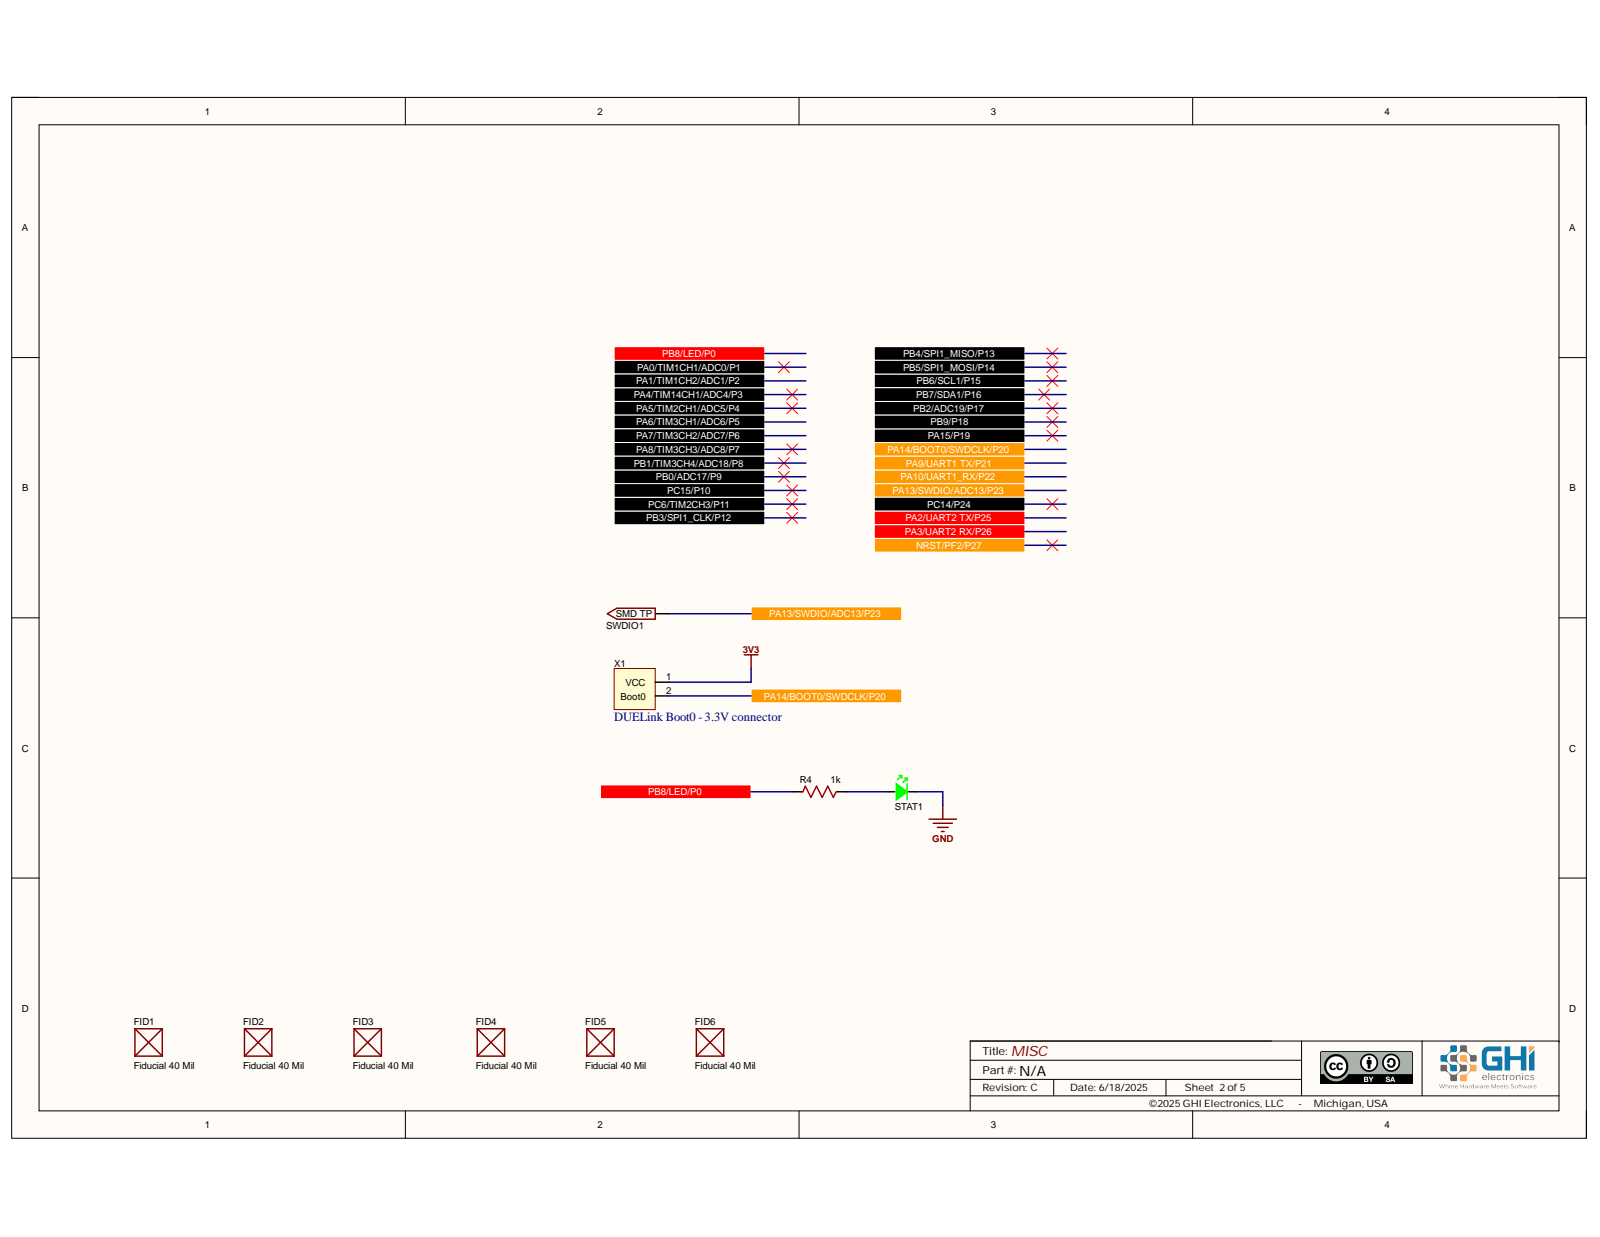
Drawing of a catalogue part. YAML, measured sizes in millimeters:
part_name: "PCB; Board; STAT1; 0603 LED Green (+4 more)"
step_written_by: "Open CASCADE 7.5 (AUTOMOTIVE_DESIGN)"
units: millimeters
bodies: {solids: 165, faces: 2469, planar: 1798, cylindrical: 417, other: 254}
overall_size: [27, 26.12, 22]
volume: 1612
surface_area: 4591
round_holes:
  - {diameter: 1, count: 9}
  - {diameter: 0.8, count: 7}
  - {diameter: 0.55, count: 4}
  - {diameter: 0.7, count: 4}
  - {diameter: 3, count: 4}
  - {diameter: 1.02, count: 2}
  - {diameter: 0.86, count: 1}
  - {diameter: 6, count: 1}
round_bosses_or_shafts:
  - {diameter: 1.1, count: 4}
  - {diameter: 11, count: 1}
  - {diameter: 9, count: 1}
  - {diameter: 0.95, count: 1}
partial_cylinders:
  - {radius: 0.12, count: 35}
  - {radius: 0.15, count: 26}
  - {radius: 0.2, count: 10}
  - {radius: 0.4, count: 9}
  - {radius: 0.9, count: 7}
  - {radius: 0.3, count: 6}
  - {radius: 0.38, count: 4}
  - {radius: 0.5, count: 4}
face_to_face_distances: [5.6, 5.8, 0.4, 1.8, 3.6, 6, 4.1, 1.3, 0.5, 5.5]
hole_center_spacings: [6.12, 12.5, 1.5, 6.74, 7.91, 14.5, 14.54, 2.62]
